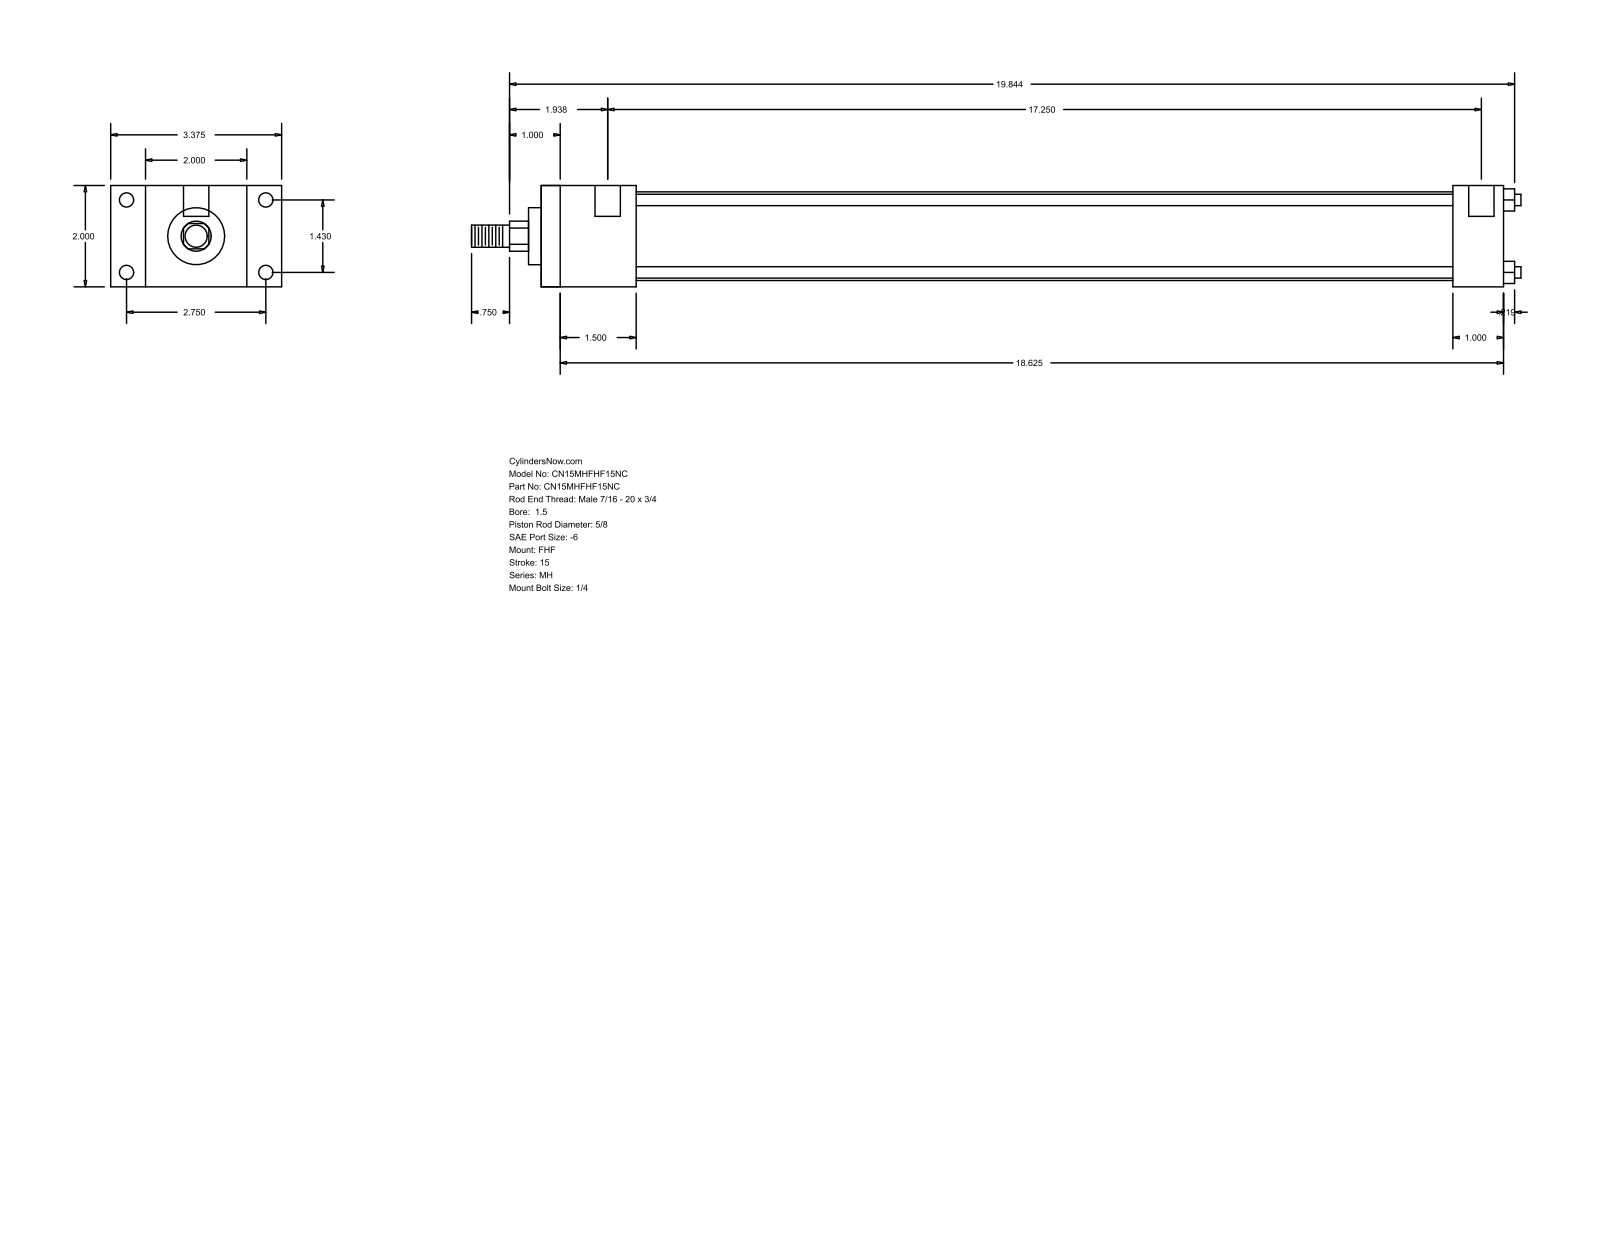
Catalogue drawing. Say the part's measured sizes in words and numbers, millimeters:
The part is named "MH_FHF__0150_0.625". Its 3-D file was written by "GSSL Pune (CONFIG_CONTROL_DESIGN)". It is 0 solids with 88 faces: 60 planar, 28 cylindrical and 0 other. Overall it measures 526.26 by 85.72 by 50.8 millimeters. Round holes: 4 of diameter 5.56, 4 of diameter 7.14, 2 of diameter 12.7. Round bosses or shafts: 4 of diameter 5.71, 1 of diameter 44.45, 1 of diameter 28.57, 1 of diameter 15.88, 1 of diameter 11.11. Partial cylindrical surfaces (rounded edges, fillets, slot ends): 1 of radius 7.54. The main face-to-face distances are 50.8, 17.46, 68.26, 47.62, 85.72, 482.6, 434.98, 457.19, 409.57, 25.41. The hole center spacings are 36.32, 69.84, 78.72, 441.32, 3.17, 438.15.
